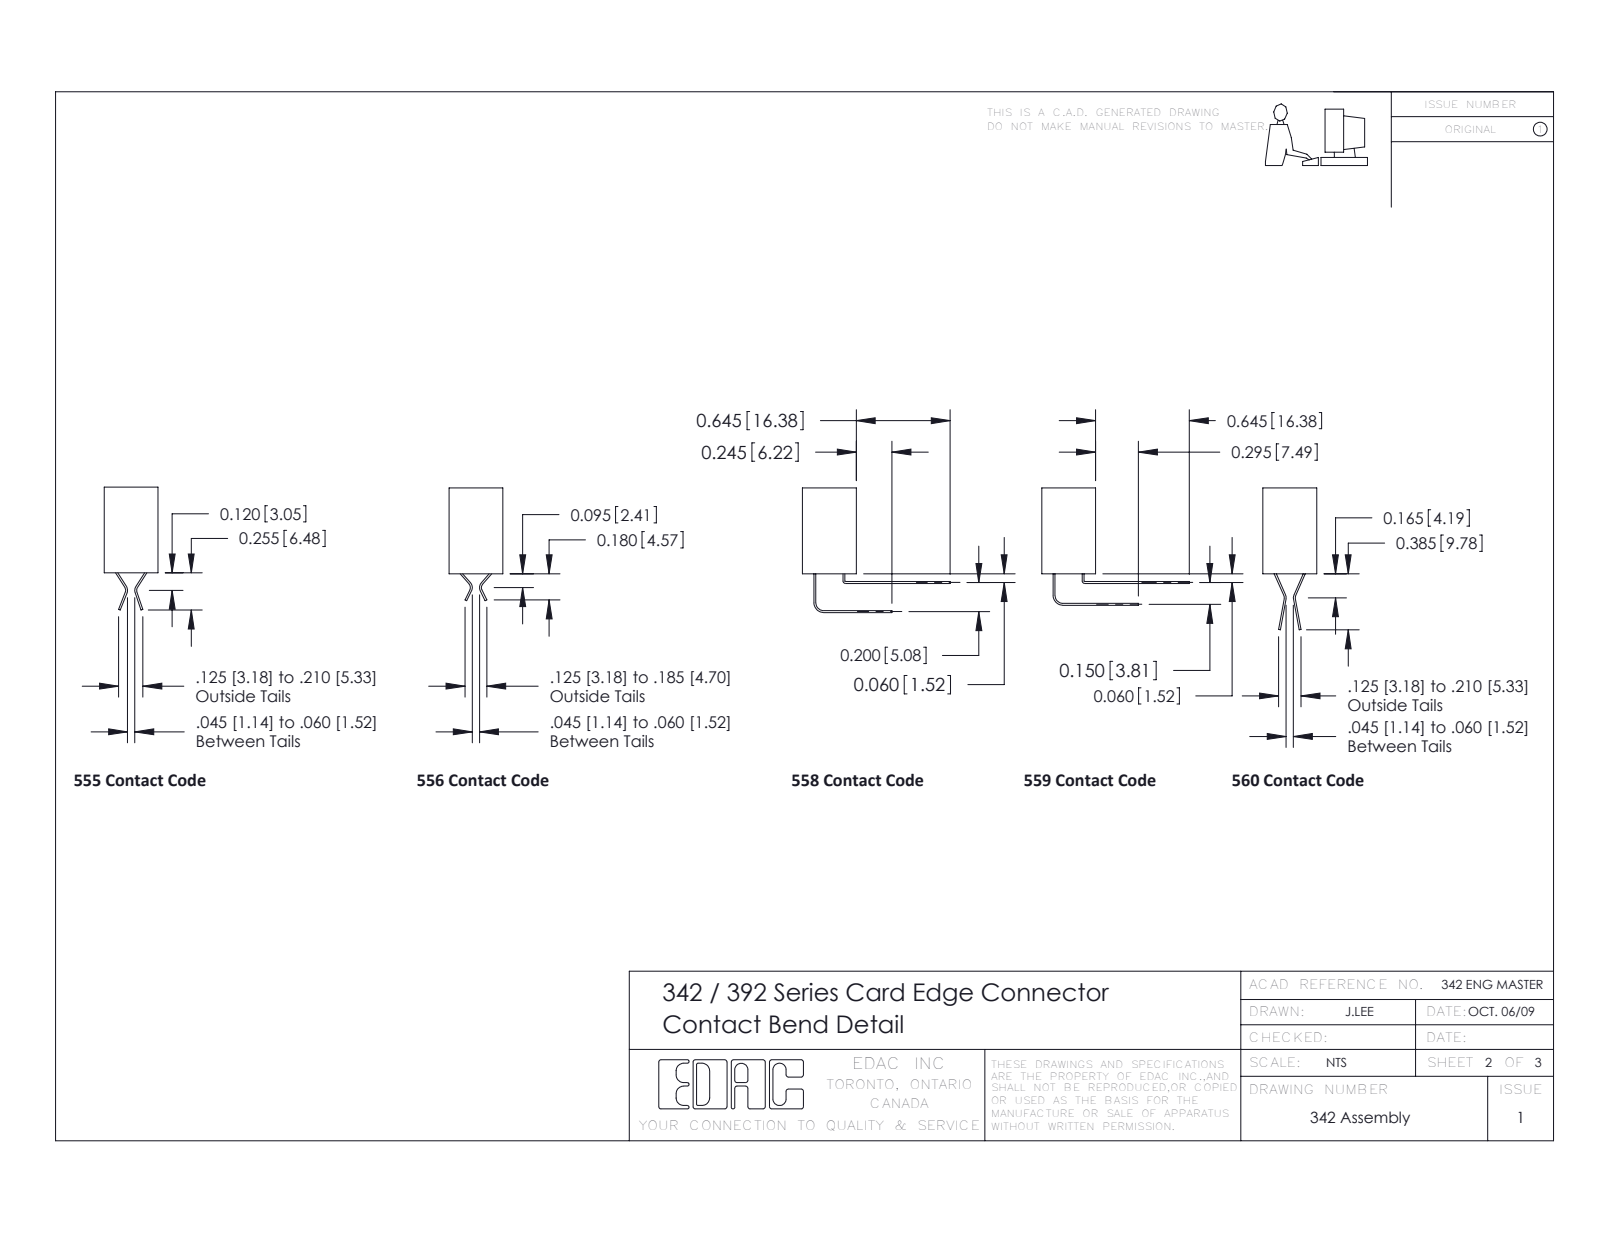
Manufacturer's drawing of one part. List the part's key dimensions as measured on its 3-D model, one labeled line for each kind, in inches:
Part name (STEP PRODUCT): 342-010-540-212; 342 Part_Side Mount; 345-292-001_345-293-140
STEP written by: SolidWorks 2016 (CONFIG_CONTROL_DESIGN)
Units: inches
Bodies: 11 solids, 630 faces (426 planar, 204 cylindrical, 0 other)
Overall size (bounding box): 1.3 × 1.16 × 0.37
Volume: 0.168 in³ · Surface area: 5.553 in²
Round holes (diameter × count): ⌀0.128 ×2
Partial cylindrical surfaces — rounded edges, fillets, slot ends (radius × count): R0.01 ×22, R0.006 ×15, R0.01 ×10, R0.007 ×6, R0.031 ×6, R0.026 ×3, R0.014 ×2, R0.022 ×2
Main face-to-face distances: 0.2, 0.1, 0.072, 0.298, 0.37, 0.04, 0.025, 0.06, 0.225, 0.098
Hole centre spacings: 1.022
